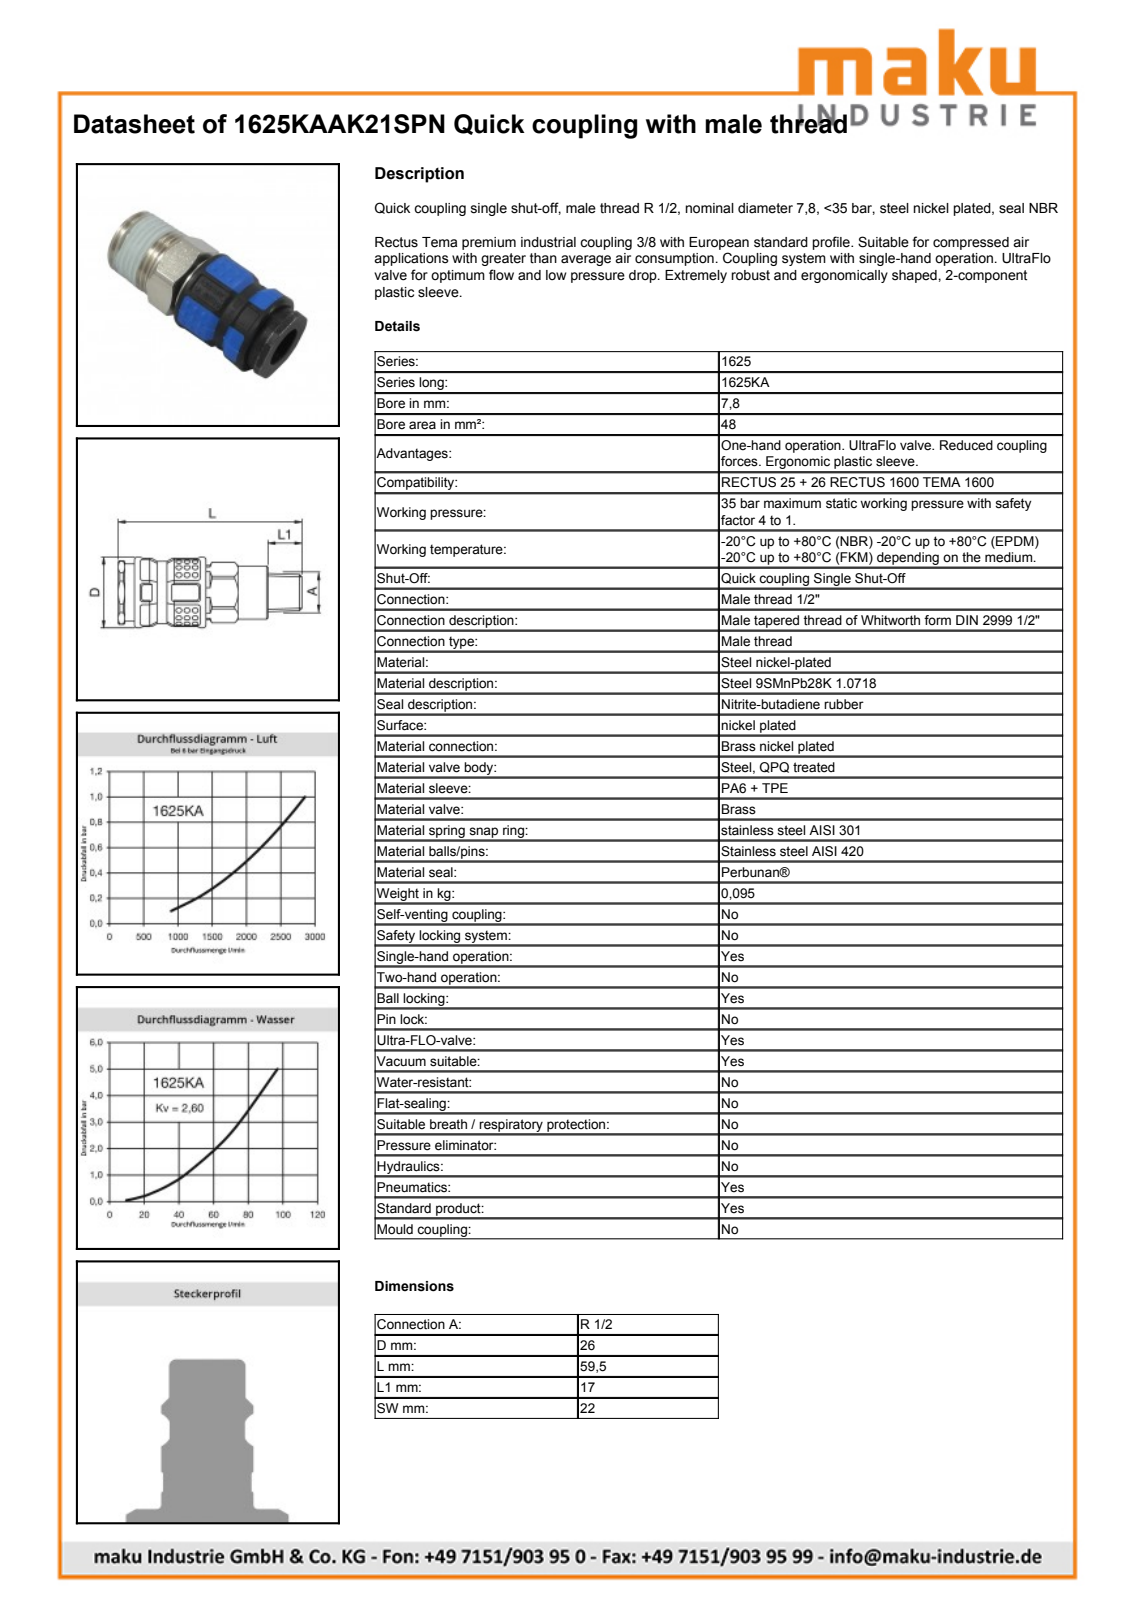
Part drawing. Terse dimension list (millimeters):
name: D105595
written by: Autodesk Inventor 2011 (AUTOMOTIVE_DESIGN)
unit: mm
bodies: 2 solids, 945 faces (351 planar, 150 cylindrical, 444 other)
size: 59.29 × 25 × 25
volume: 22 520 mm³; area: 9 488 mm²
holes: 4× ⌀1, 1× ⌀16.15, 1× ⌀17.2, 1× ⌀17.9, 1× ⌀19.6, 1× ⌀20.7
bosses: 1× ⌀25, 1× ⌀22, 1× ⌀20.3, 1× ⌀19.3, 1× ⌀17.6, 1× ⌀17, 1× ⌀15.7, 1× ⌀15.6
rounds: 8× R0.4, 1× R11.2, 1× R11.25, 1× R11.5, 1× R12, 1× R12.3, 1× R12.4
face distances: 22, 59.29, 30.93, 28.36, 25.3, 5.63, 53.66, 26.79, 32.5, 4.14
hole spacings: 12.8
